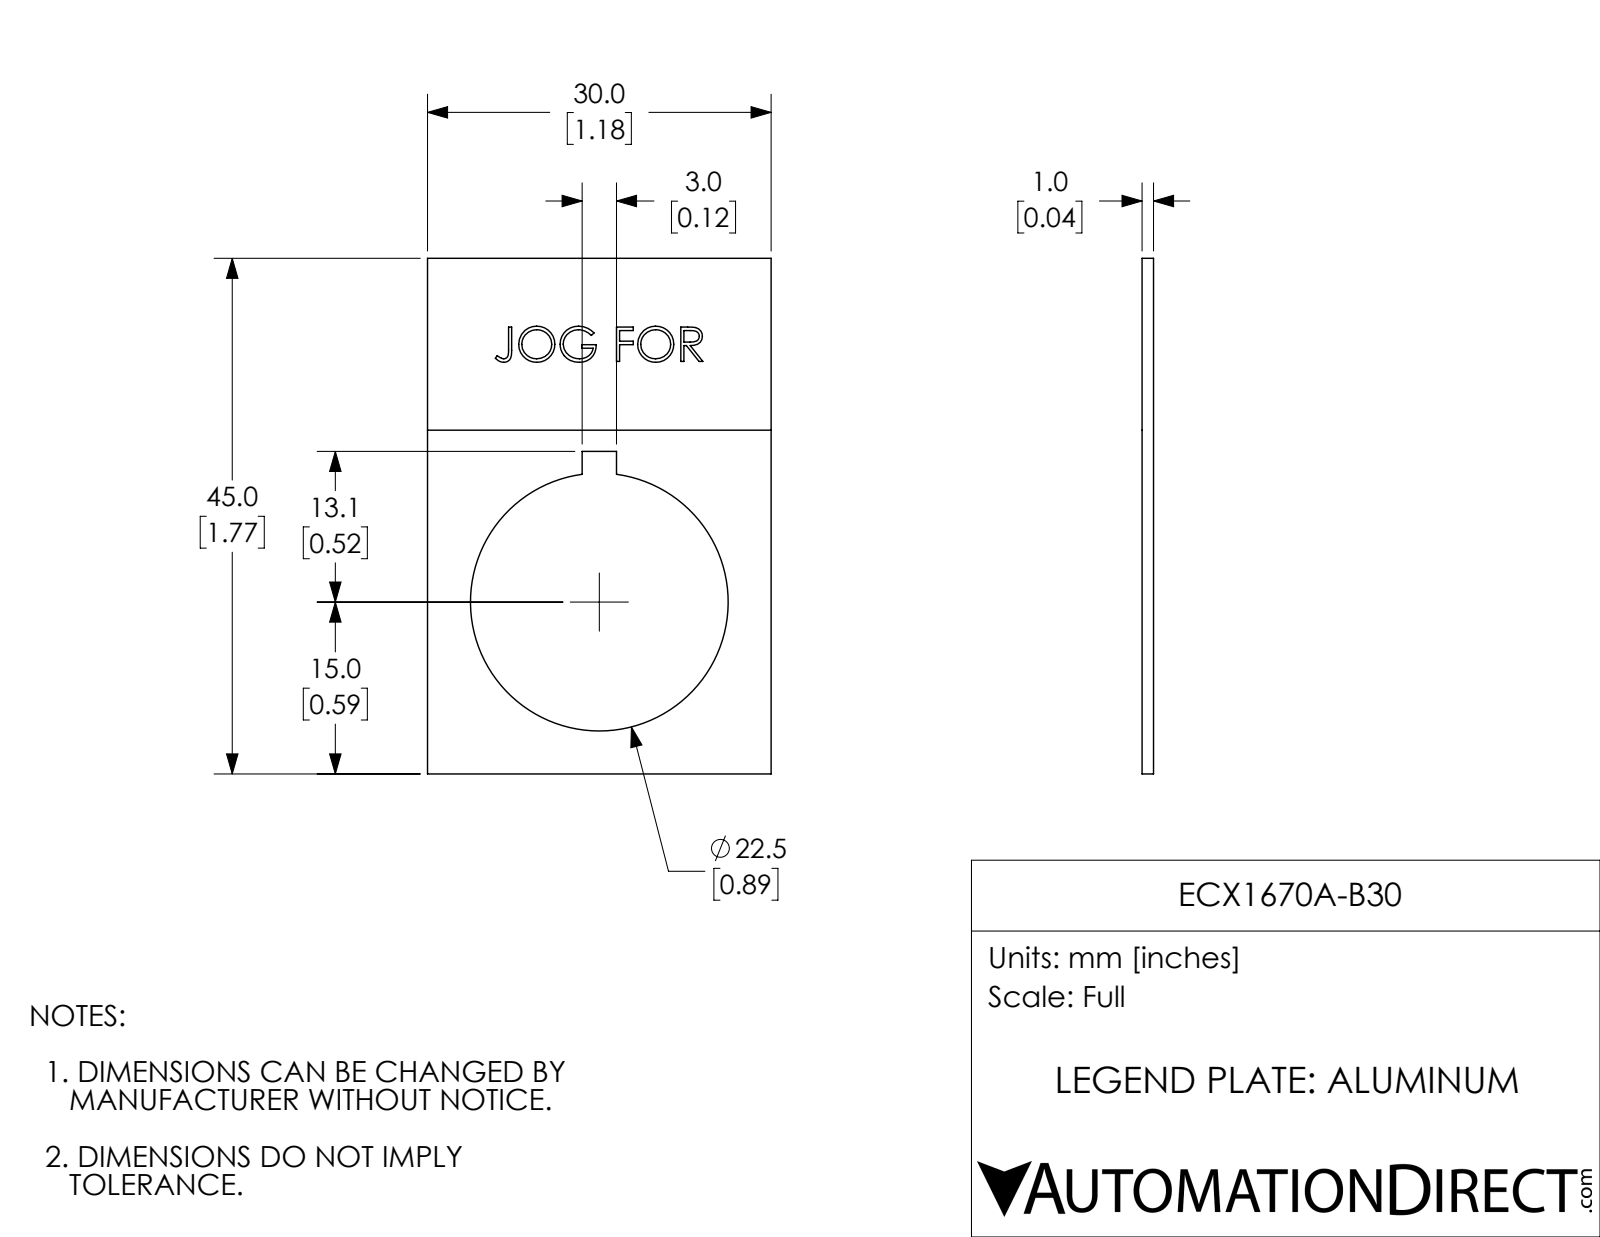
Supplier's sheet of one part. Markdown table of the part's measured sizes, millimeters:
| quantity | value |
| --- | --- |
| part name | ECX1670A-B30 |
| STEP written by | SolidWorks 2017 (AUTOMOTIVE_DESIGN) |
| units | millimeters |
| bodies | 1 solid, 86 faces (48 planar, 3 cylindrical, 35 other) |
| overall size | 45 × 30 × 1 |
| volume | 950 mm³ |
| surface area | 2 120 mm² |
| round holes (diameter × count) | 22.5 × 1 |
| main face-to-face distances | 1, 30, 45, 1, 13.5, 16.5, 28.1, 16.8, 3, 9.4 |
